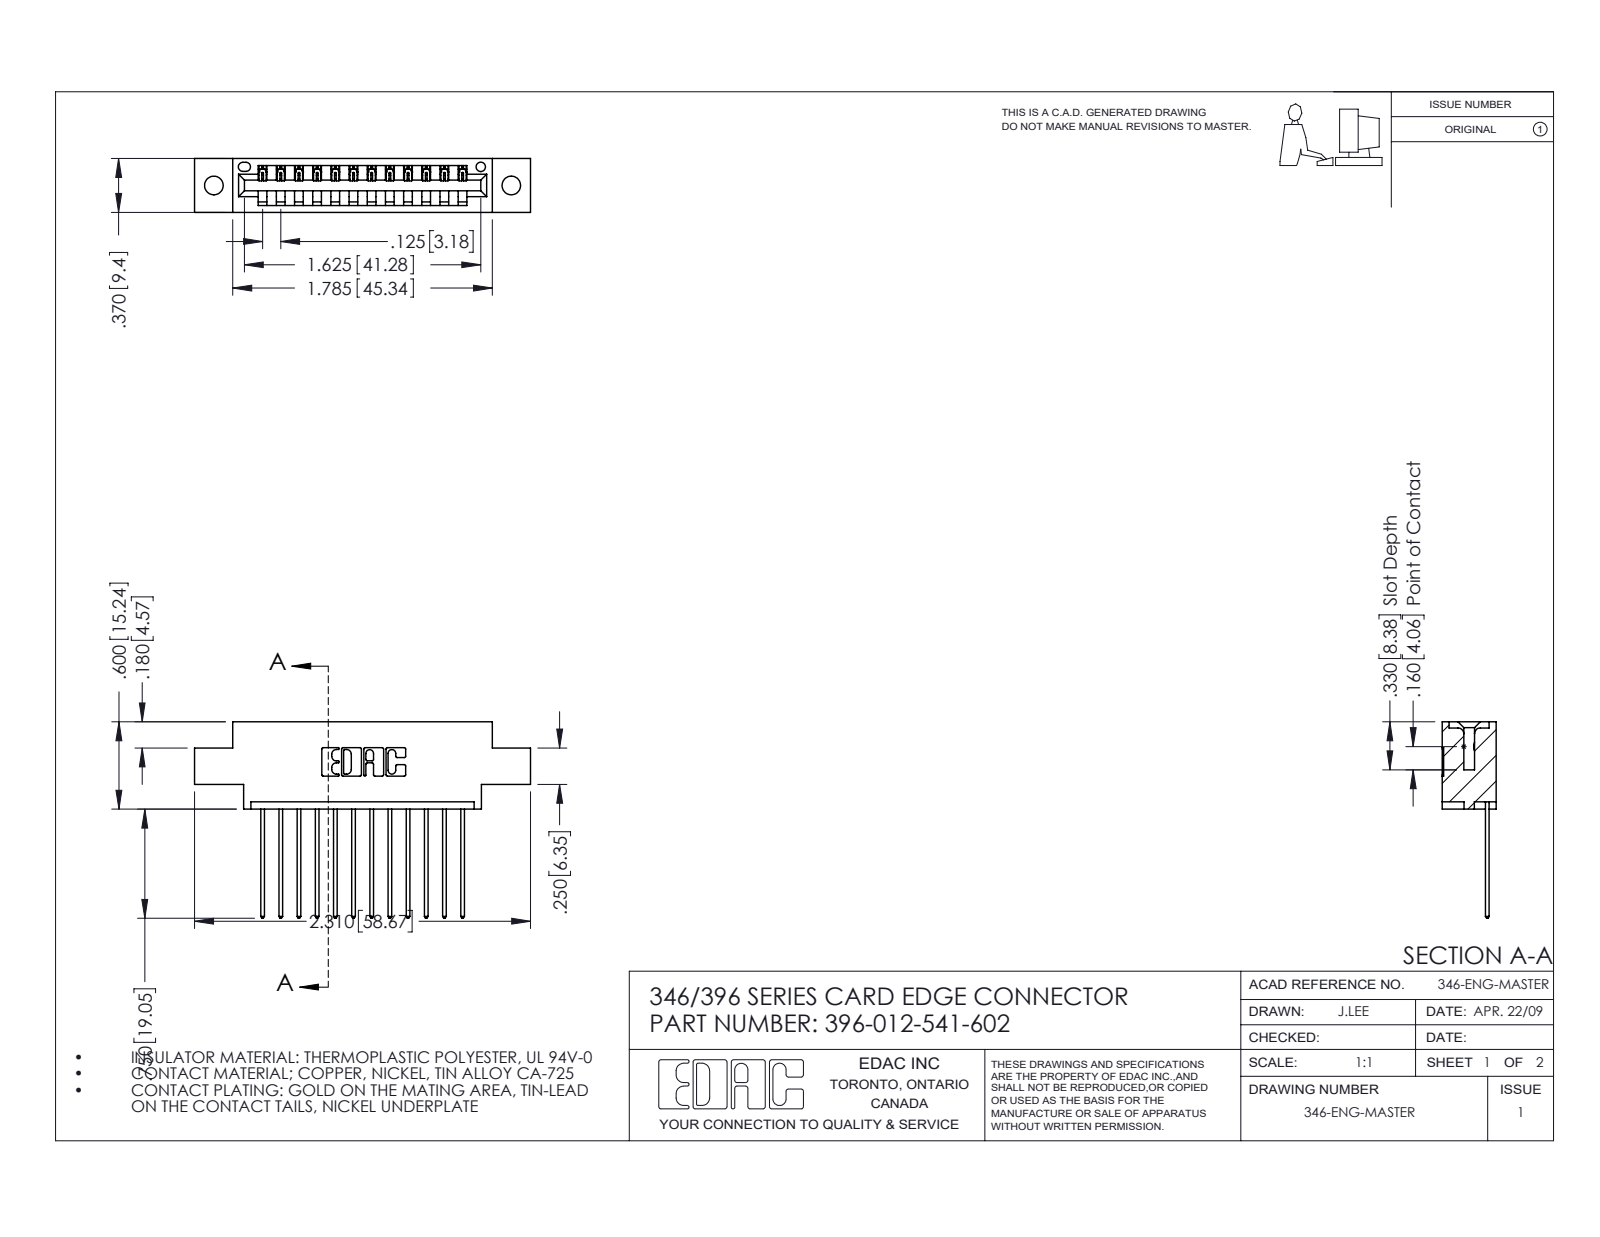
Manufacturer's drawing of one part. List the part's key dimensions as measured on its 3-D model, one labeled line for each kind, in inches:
Part name (STEP PRODUCT): 396-012-541-602; 346 Part_0.170 Offset - 0.128 Dia; 345-292-001_345-293-141
STEP written by: SolidWorks 2016 (CONFIG_CONTROL_DESIGN)
Units: inches
Bodies: 13 solids, 822 faces (560 planar, 262 cylindrical, 0 other)
Overall size (bounding box): 2.31 × 1.35 × 0.37
Volume: 0.321 in³ · Surface area: 9.879 in²
Round holes (diameter × count): ⌀0.128 ×2, ⌀0.064 ×1
Partial cylindrical surfaces — rounded edges, fillets, slot ends (radius × count): R0.006 ×24, R0.01 ×24, R0.01 ×22, R0.007 ×6, R0.031 ×6, R0.026 ×3, R0.031 ×2, R0.04 ×2
Main face-to-face distances: 0.25, 0.048, 0.322, 0.37, 0.072, 0.298, 0.025, 0.148, 0.222, 0.1
Hole centre spacings: 0.246, 1.839, 2.045
